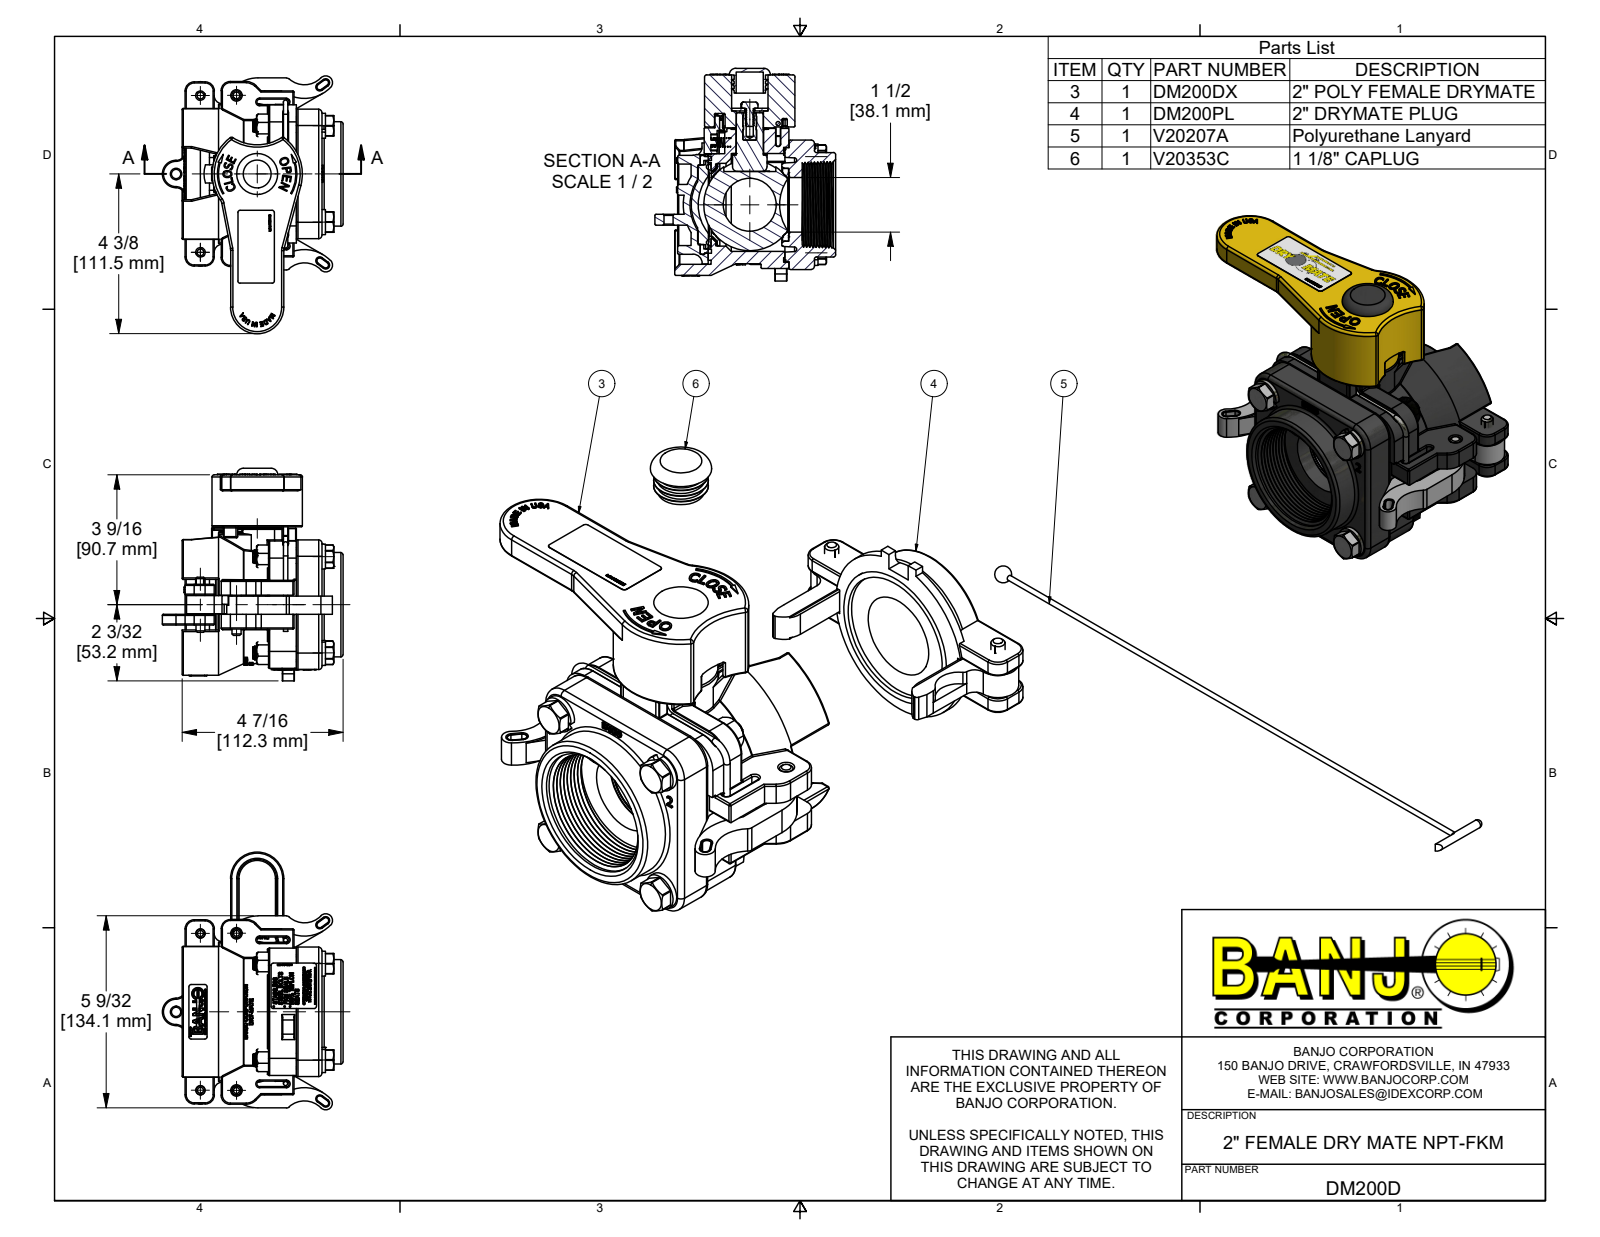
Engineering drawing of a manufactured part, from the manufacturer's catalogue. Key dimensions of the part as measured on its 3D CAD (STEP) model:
Part name (STEP PRODUCT): DM200D; DM200DX; DM20254F; DM20254FY (+8 more)
STEP written by: Autodesk Inventor 2022 (AUTOMOTIVE_DESIGN)
Units: inches
Bodies: 44 solids, 6596 faces (3043 planar, 1046 cylindrical, 2507 other)
Overall size (bounding box): 7.084 × 5.845 × 4.967
Volume: 45.32 in³ · Surface area: 403.6 in²
Round holes (diameter × count): ⌀0.25 ×5, ⌀0.375 ×5, ⌀0.256 ×4, ⌀0.307 ×4, ⌀0.385 ×4, ⌀0.41 ×4, ⌀0.42 ×4, ⌀0.125 ×3, ⌀0.196 ×1, ⌀0.2 ×1, ⌀0.227 ×1, ⌀0.281 ×1
Round bosses / shafts (diameter × count): ⌀0.324 ×60, ⌀0.12 ×5, ⌀0.687 ×4, ⌀0.375 ×4, ⌀0.26 ×4, ⌀0.249 ×4, ⌀0.28 ×3, ⌀3.25 ×1
Partial cylindrical surfaces — rounded edges, fillets, slot ends (radius × count): R0.03 ×159, R0.01 ×41, R0.06 ×35, R0.02 ×20, R0.25 ×11, R0.12 ×10, R0.08 ×8, R0.09 ×8
Main face-to-face distances: 0.92, 0.11, 2.217, 0.298, 0.013, 0.5, 0.08, 0.7, 3.833, 3.142
Hole centre spacings: 2.654, 1.872, 1.881, 2.648, 2.66, 3.753, 0.95, 0.992
